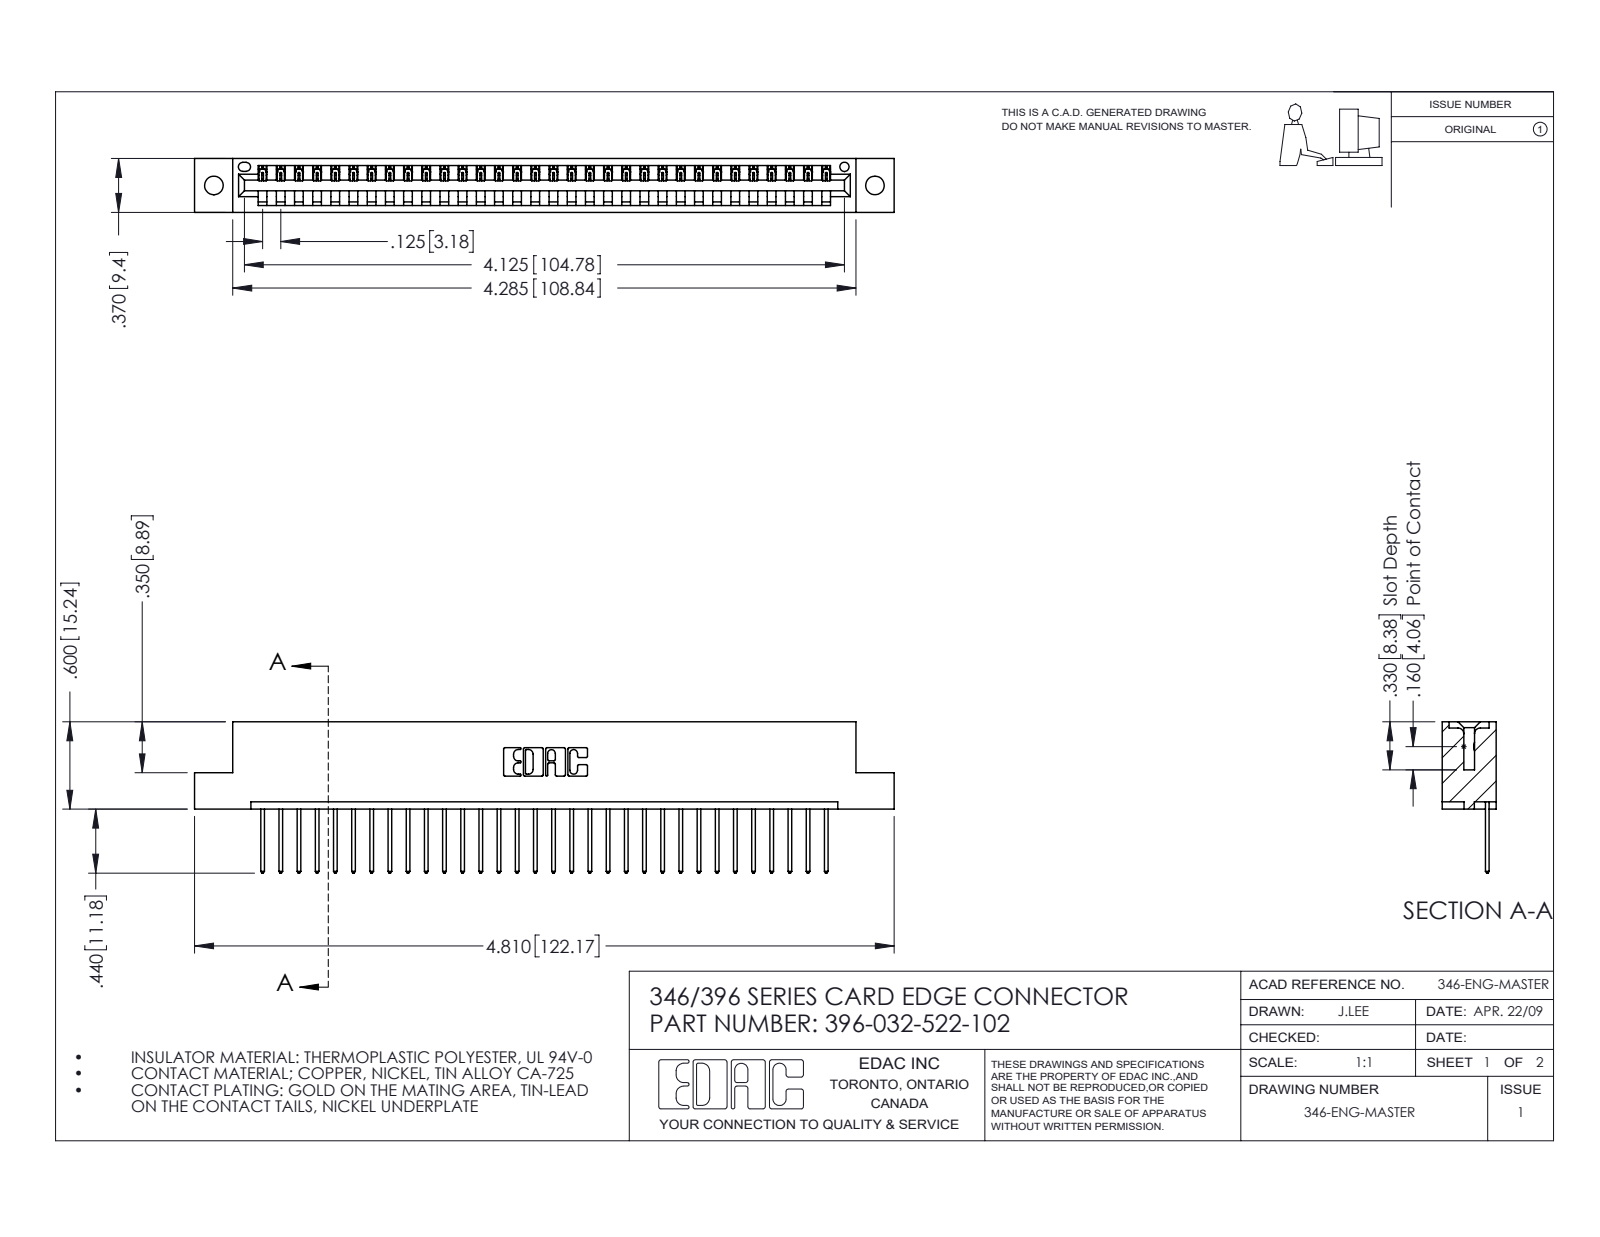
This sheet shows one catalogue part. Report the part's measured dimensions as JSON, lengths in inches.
{"part_name": "396-032-522-102; 345-292-001_345-293-122; 346 Part_Flush Mounting Lugs - 0.128 Dia", "step_written_by": "SolidWorks 2016 (CONFIG_CONTROL_DESIGN)", "units": "inches", "bodies": {"solids": 33, "faces": 1978, "planar": 1356, "cylindrical": 622, "other": 0}, "overall_size": [4.81, 1.04, 0.37], "volume_in3": 0.707, "surface_area_in2": 22.05, "round_holes": [[0.128, 2], [0.064, 1]], "partial_cylinders_radius": [[0.006, 64], [0.01, 64], [0.01, 22], [0.007, 6], [0.031, 6], [0.026, 3], [0.031, 2], [0.04, 2]], "face_to_face_distances": [0.048, 0.322, 0.37, 0.25, 0.072, 0.298, 0.025, 0.148, 0.222, 0.1], "hole_center_spacings": [0.246, 4.337, 4.545]}
